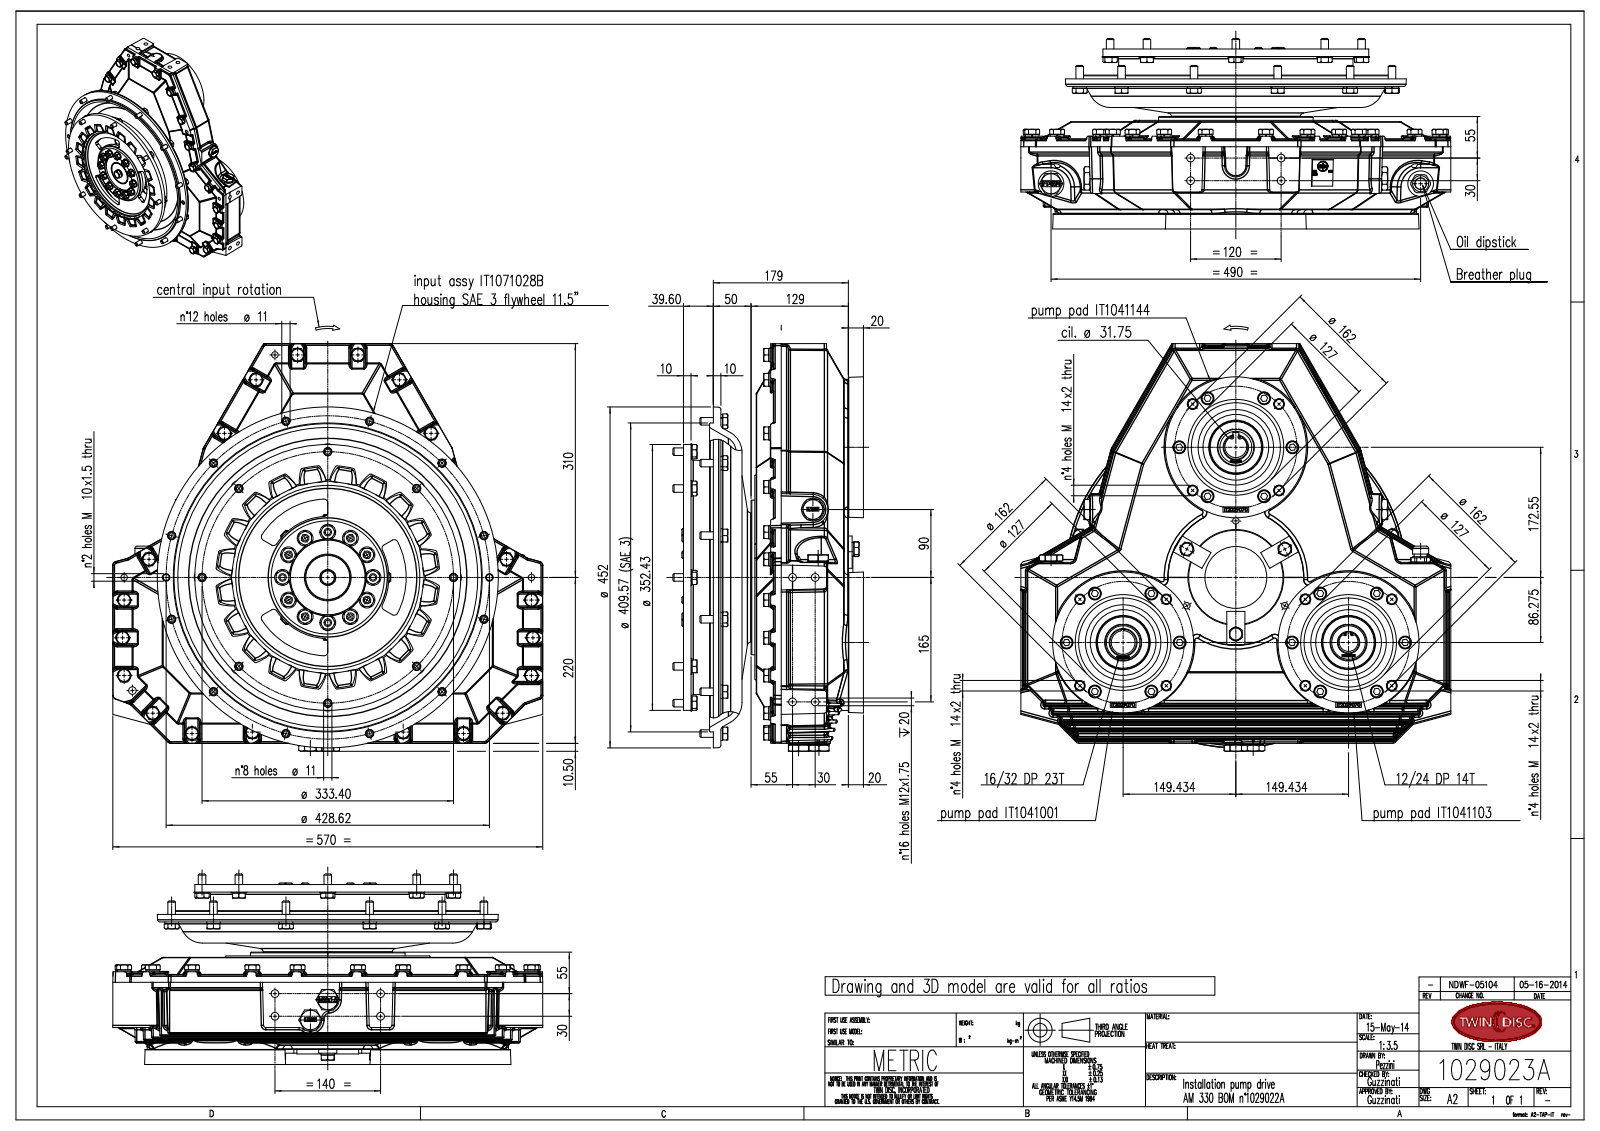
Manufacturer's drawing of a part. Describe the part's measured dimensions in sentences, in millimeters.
The part is named "IT1041001_rev01-installation; ITam220-002_rev00-installation; IT0000200_rev00-installation; IT1071028B_rev02-installation (+6 more)". Its 3-D file was written by "SolidWorks 2007 (AUTOMOTIVE_DESIGN)". It is 80 solids with 10307 faces: 3776 planar, 3315 cylindrical and 3216 other. Overall it measures 570 by 565.04 by 252.6 millimeters. Its volume is 25 380 000 cubic millimeters and its surface area 2 560 000 square millimeters. Round holes: 67 of diameter 10.2, 61 of diameter 8.5, 54 of diameter 10.5, 33 of diameter 11, 18 of diameter 17, 12 of diameter 12, 8 of diameter 14, 4 of diameter 100, 4 of diameter 107.93, 4 of diameter 125, 3 of diameter 8, 3 of diameter 18.5. Round bosses or shafts: 88 of diameter 10, 68 of diameter 16.2, 48 of diameter 18.1, 20 of diameter 21, 18 of diameter 16, 4 of diameter 87.07, 4 of diameter 70, 4 of diameter 14. Partial cylindrical surfaces (rounded edges, fillets, slot ends): 344 of radius 2, 163 of radius 3, 86 of radius 5, 80 of radius 1, 80 of radius 4, 42 of radius 2.5, 40 of radius 42.91, 12 of radius 1.5. The main face-to-face distances are 149, 20, 169, 27, 122, 30, 50, 11.5, 8, 10. The hole center spacings are 214.31, 303.08, 371.2, 414.02, 75, 110.93, 30, 143.19.
